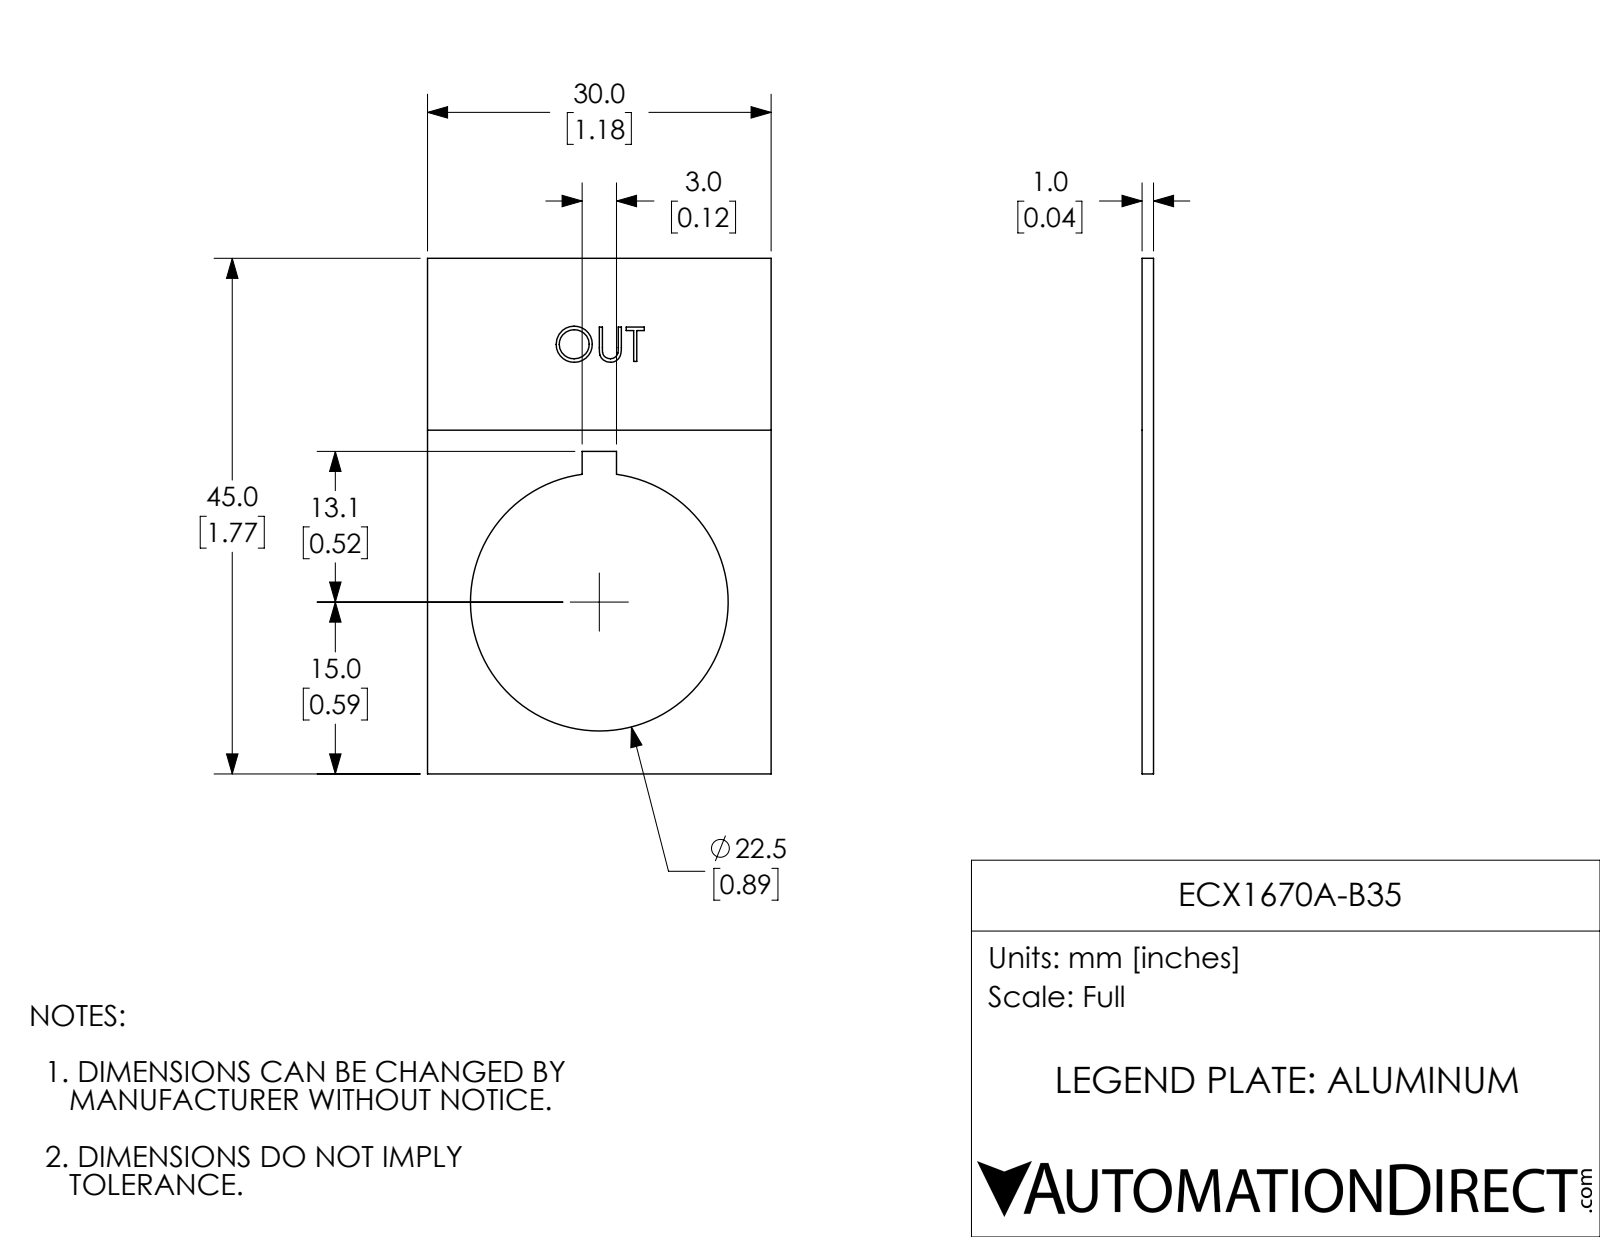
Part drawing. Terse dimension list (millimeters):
name: ECX1670A-B35
written by: SolidWorks 2017 (AUTOMOTIVE_DESIGN)
unit: mm
bodies: 1 solid, 46 faces (28 planar, 3 cylindrical, 15 other)
size: 45 × 30 × 1
volume: 950 mm³; area: 2 119 mm²
holes: 1× ⌀22.5
face distances: 1, 30, 45, 1, 13.5, 16.5, 28.1, 16.8, 3, 1.5
